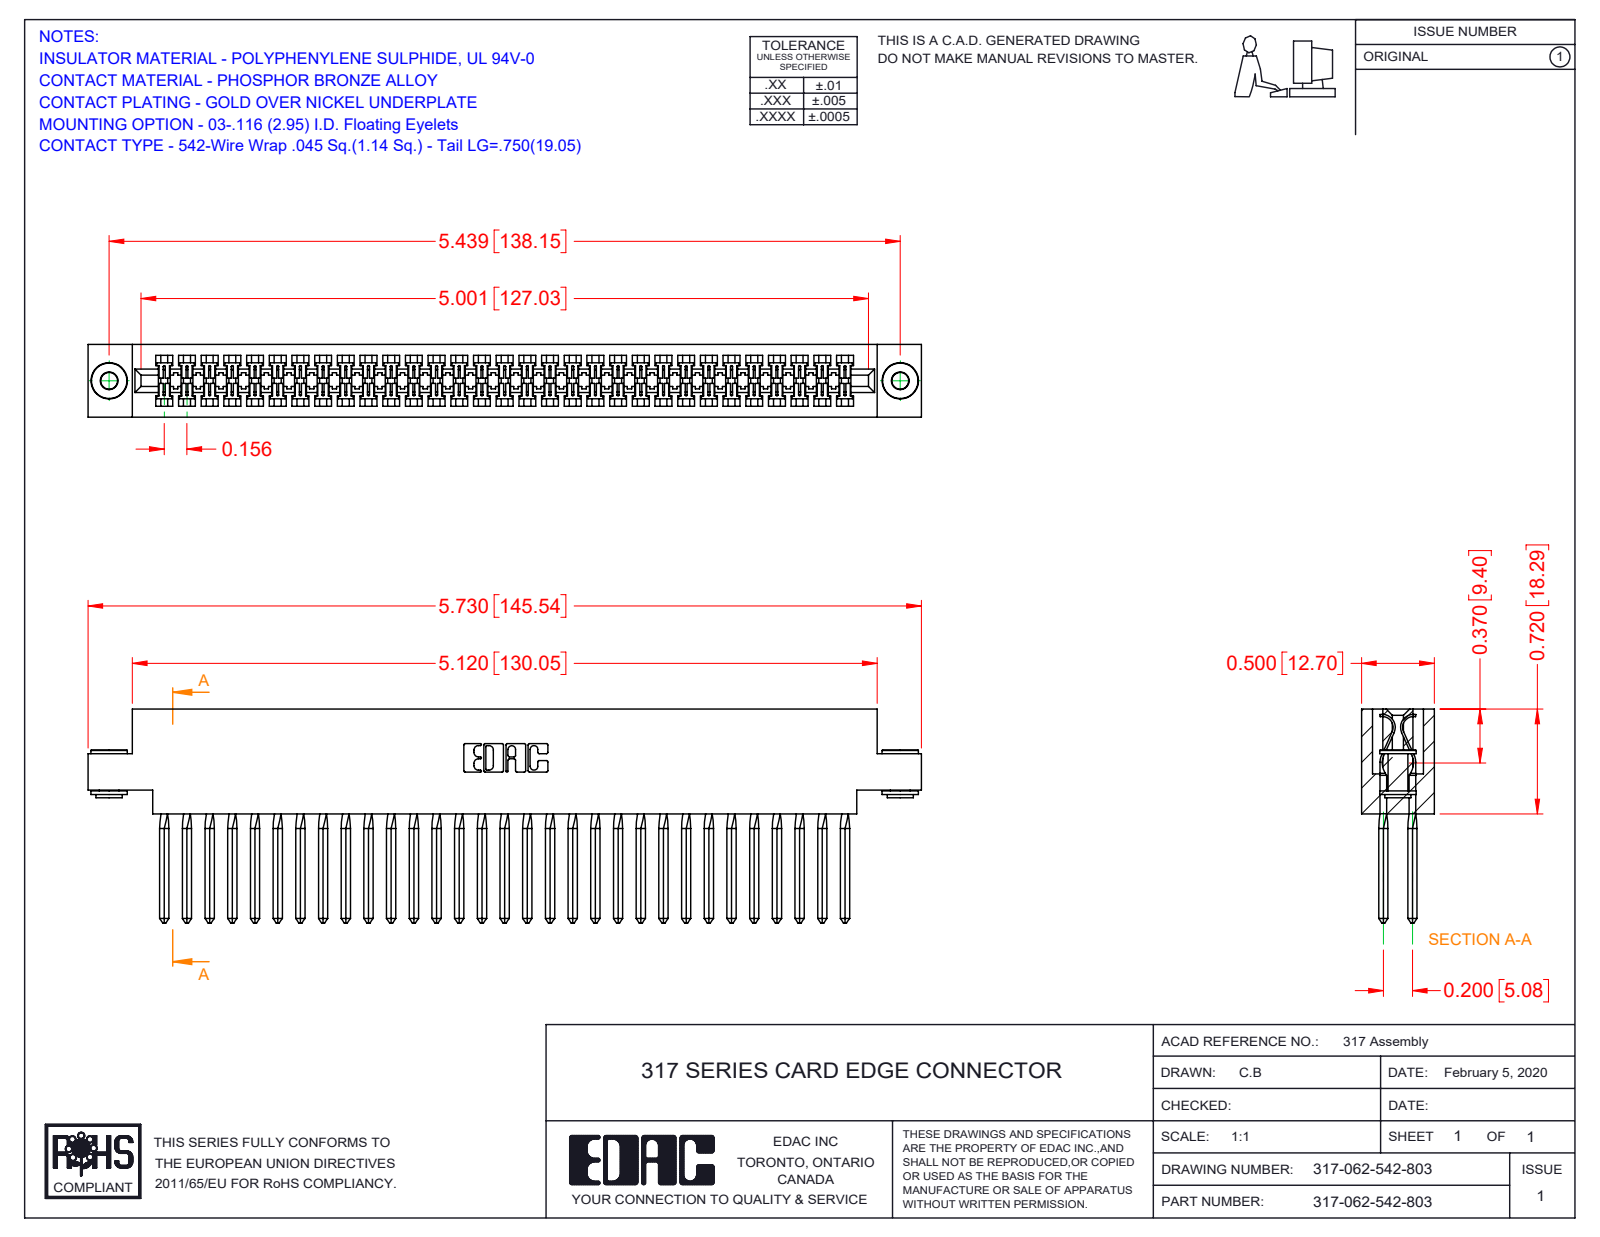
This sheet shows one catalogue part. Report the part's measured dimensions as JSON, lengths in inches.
{"part_name": "345-250-002_345-250-002-102; 317-062-542-803; 317-290-003_542; 317 Part_.156 Dia - TH", "step_written_by": "SolidWorks 2016 (CONFIG_CONTROL_DESIGN)", "units": "inches", "bodies": {"solids": 65, "faces": 3674, "planar": 2920, "cylindrical": 498, "other": 256}, "overall_size": [5.73, 1.47, 0.5], "volume_in3": 1.434, "surface_area_in2": 50.45, "round_holes": [[0.116, 2], [0.156, 2]], "round_bosses_or_shafts": [[0.25, 2], [0.18, 2], [0.136, 2]], "partial_cylinders_radius": [[0.006, 124], [0.01, 22], [0.007, 6], [0.031, 6], [0.026, 3], [0.074, 2], [0.089, 2], [0.1, 2]], "face_to_face_distances": [0.5, 0.075, 0.425, 0.35, 0.2, 0.11, 0.116, 0.046, 0.128, 0.372], "hole_center_spacings": [5.439]}
